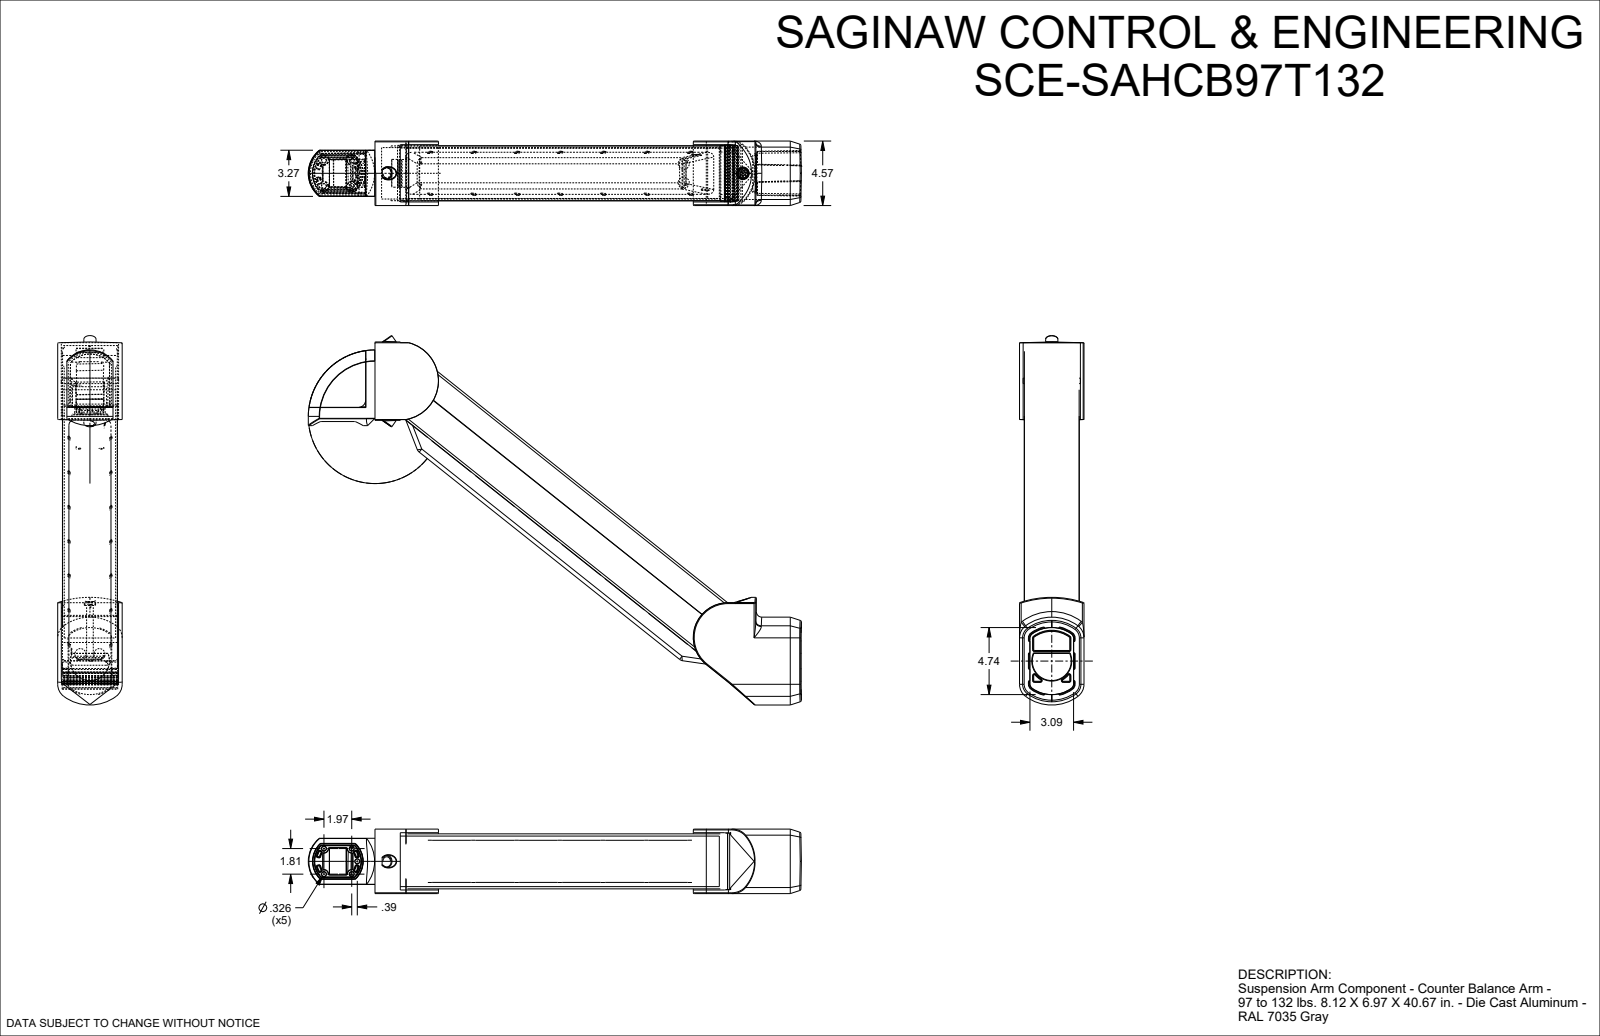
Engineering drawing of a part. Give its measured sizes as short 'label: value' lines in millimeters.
name: SCE-SAHCB97T132
written by: SolidWorks 2023 (AUTOMOTIVE_DESIGN)
unit: mm
bodies: 7 solids, 951 faces (343 planar, 274 cylindrical, 334 other)
size: 887.1 × 664.2 × 116
volume: 15 660 000 mm³; area: 963 200 mm²
bosses: 3× ⌀20, 1× ⌀18, 1× ⌀12
rounds: 97× R1, 30× R1.5, 14× R0.5, 13× R3, 10× R12, 8× R2.5, 4× R2, 4× R4
face distances: 72, 58, 8.6, 107.4, 8.7, 107.2, 98.7, 58.3, 95.5, 3
